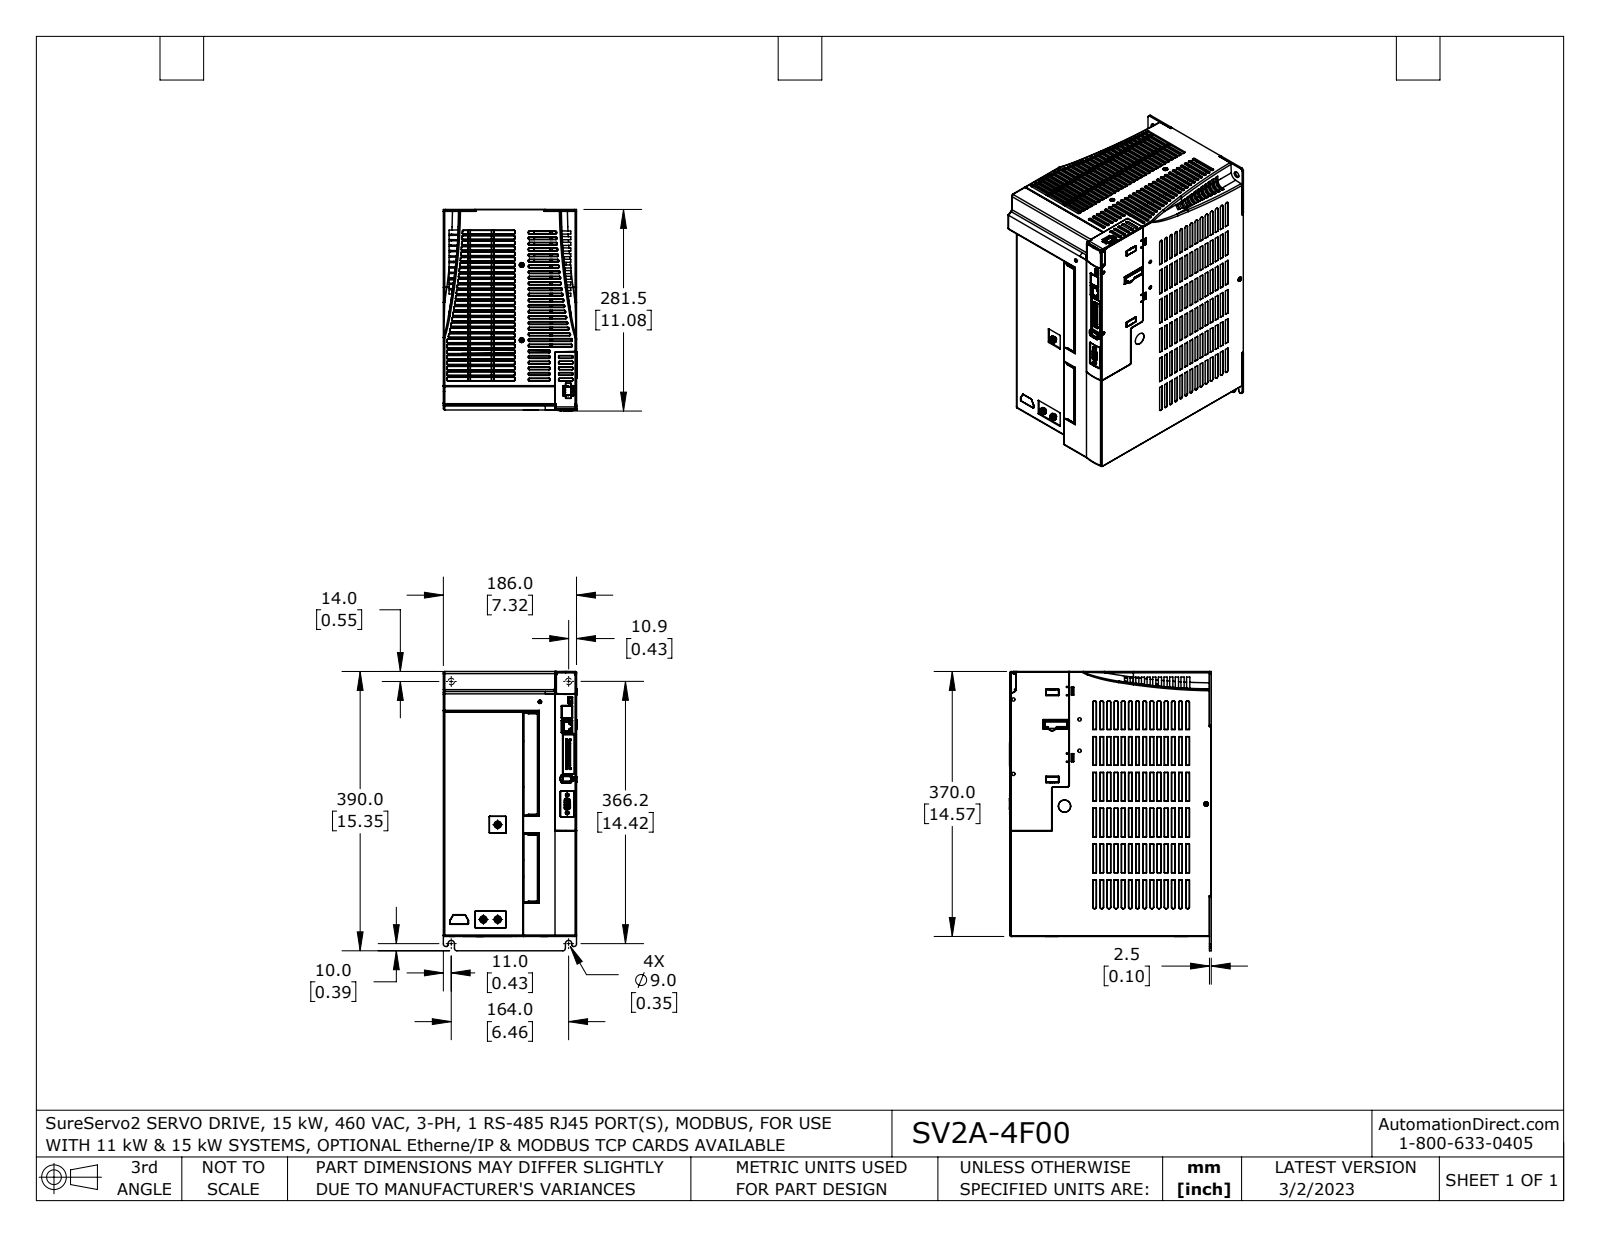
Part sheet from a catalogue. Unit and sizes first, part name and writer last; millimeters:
Units: millimetres
Overall size (bounding box): 390 × 282.5 × 187
Round holes (diameter × count): ⌀1.1 ×15, ⌀5 ×10, ⌀8.4 ×8, ⌀9.8 ×4, ⌀5.5 ×3, ⌀1.7 ×2, ⌀3 ×2, ⌀9 ×2, ⌀47.3 ×2, ⌀62.5 ×2, ⌀77.7 ×2, ⌀1.6 ×1
Round bosses / shafts (diameter × count): ⌀8 ×10, ⌀4 ×6, ⌀10 ×3, ⌀9 ×3, ⌀5 ×3, ⌀81.5 ×2, ⌀66.3 ×2, ⌀50.5 ×2
Partial cylindrical surfaces — rounded edges, fillets, slot ends (radius × count): R0.3 ×60, R0.2 ×50, R0.5 ×48, R0.1 ×28, R1.5 ×17, R2 ×17, R0.7 ×10, R2.5 ×10
Main face-to-face distances: 186, 186, 370, 185.9, 263.5, 280, 263.4, 280, 16.5, 370
Hole centre spacings: 2.3, 4, 2.3, 4.6, 6, 4.6, 4, 6.9
Volume: 18 520 000 mm³ · Surface area: 496 800 mm²
Bodies: 1 solid, 3970 faces (2192 planar, 893 cylindrical, 885 other)
Part name (STEP PRODUCT): SV2A-4F00_3D_All_20200930 1st Ext Coord comb 3C red1 ext1mod1 Cb 7faces EXT 1 x2r1 comb 2 r1b red1 M1C2bcnl m1Bb
STEP written by: SolidWorks 2021 (AUTOMOTIVE_DESIGN)
